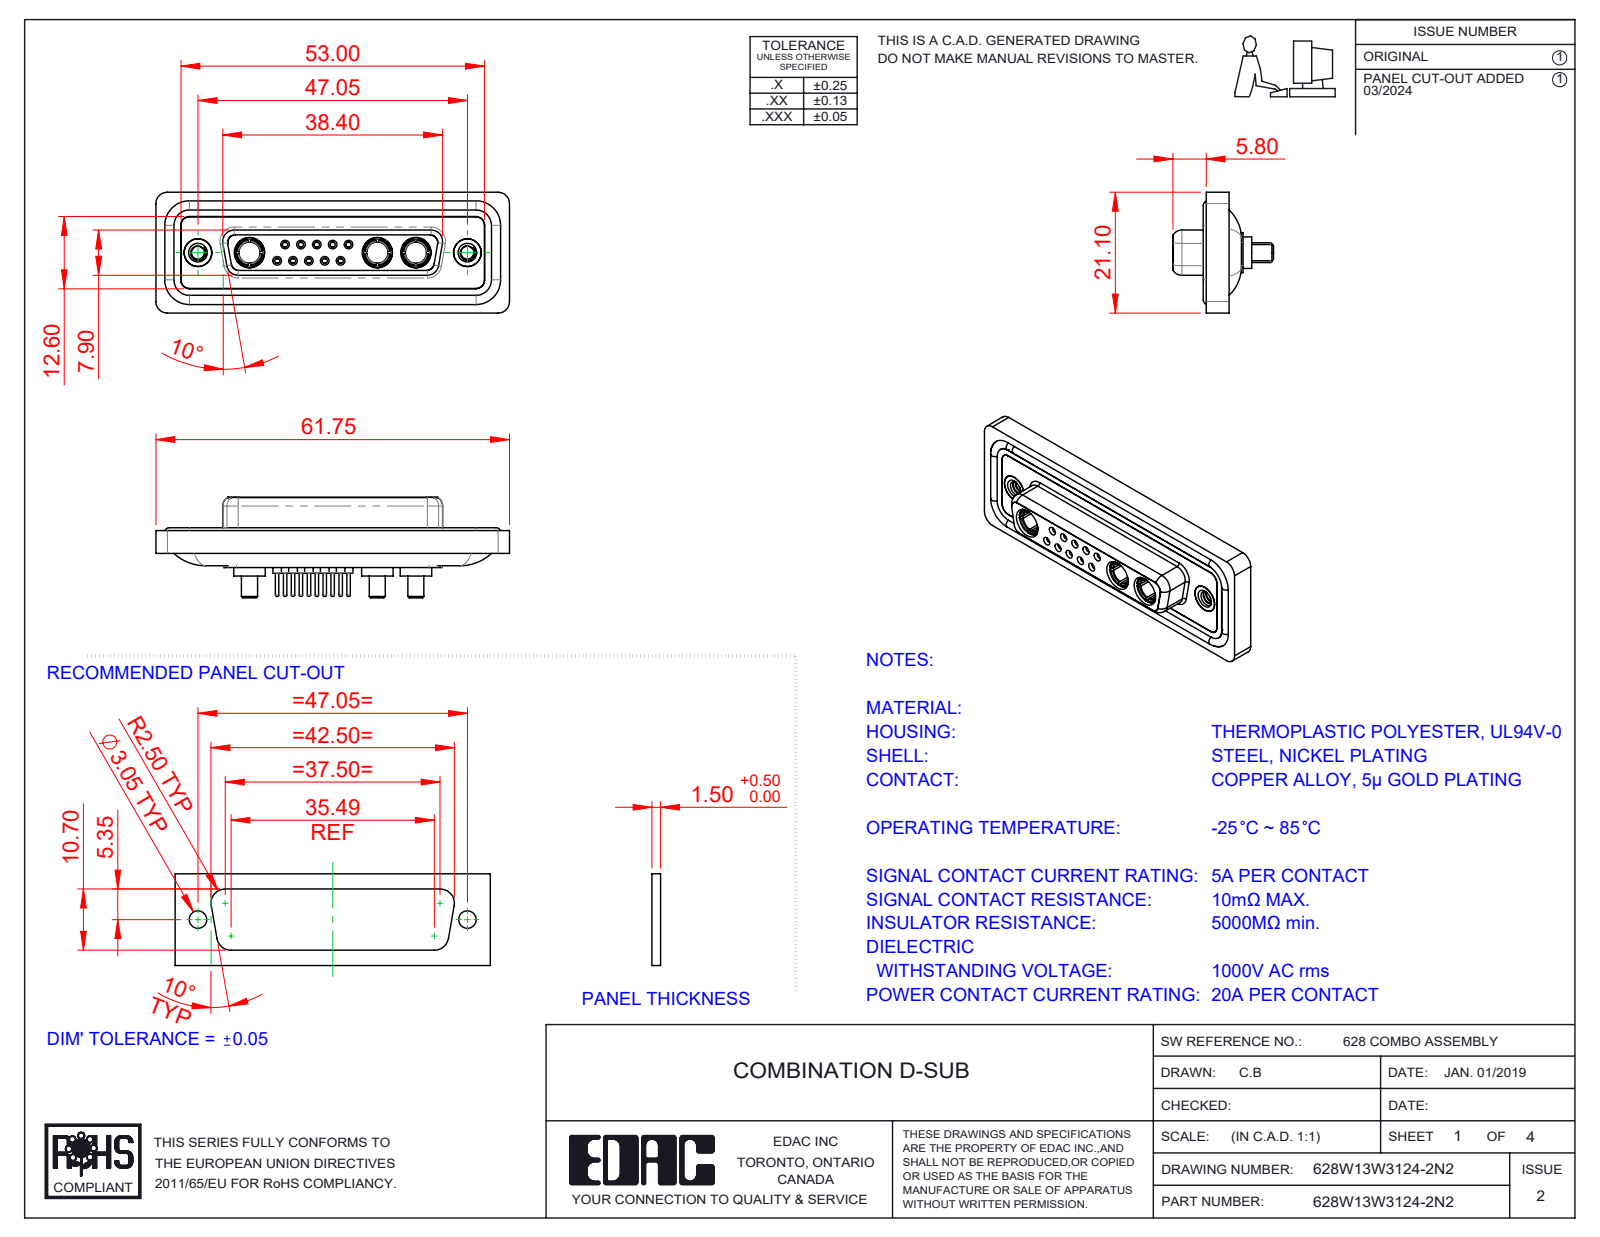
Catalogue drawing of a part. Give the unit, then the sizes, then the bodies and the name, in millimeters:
Units: millimetres
Overall size (bounding box): 61.75 × 21.1 × 17.55
Round holes (diameter × count): ⌀0.9 ×10, ⌀1.1 ×10, ⌀1.5 ×10, ⌀2 ×10, ⌀1.6 ×5, ⌀1.7 ×5, ⌀4.85 ×5, ⌀3.7 ×3, ⌀5.3 ×3, ⌀2.26 ×2, ⌀4 ×2, ⌀4.05 ×2
Round bosses / shafts (diameter × count): ⌀2.2 ×10, ⌀0.6 ×10, ⌀1.6 ×9, ⌀5.5 ×3, ⌀5.2 ×3, ⌀4.96 ×3, ⌀4.75 ×3, ⌀3.75 ×3
Partial cylindrical surfaces — rounded edges, fillets, slot ends (radius × count): R1.5 ×22, R2 ×18, R1.35 ×8, R1.6 ×8, R0.25 ×4, R0.5 ×4, R0.6 ×4, R0.65 ×4
Main face-to-face distances: 0.4, 1.8, 7.45, 5.65, 0.5, 6.6, 7.05, 1.6, 2.9, 1.1
Hole centre spacings: 3.16, 2.77, 5.03, 5.04, 5.54, 8.31, 7.49, 2.76
Volume: 8 273 mm³ · Surface area: 13 709 mm²
Bodies: 23 solids, 1158 faces (342 planar, 447 cylindrical, 369 other)
Part name (STEP PRODUCT): 628Combo Threaded Rivet_2; 628W13W3124-2N2; 628Combo Contact Row 1_24; 628Combo Shell Front_25 Contacts (+5 more)
STEP written by: SolidWorks 2023 (CONFIG_CONTROL_DESIGN)
